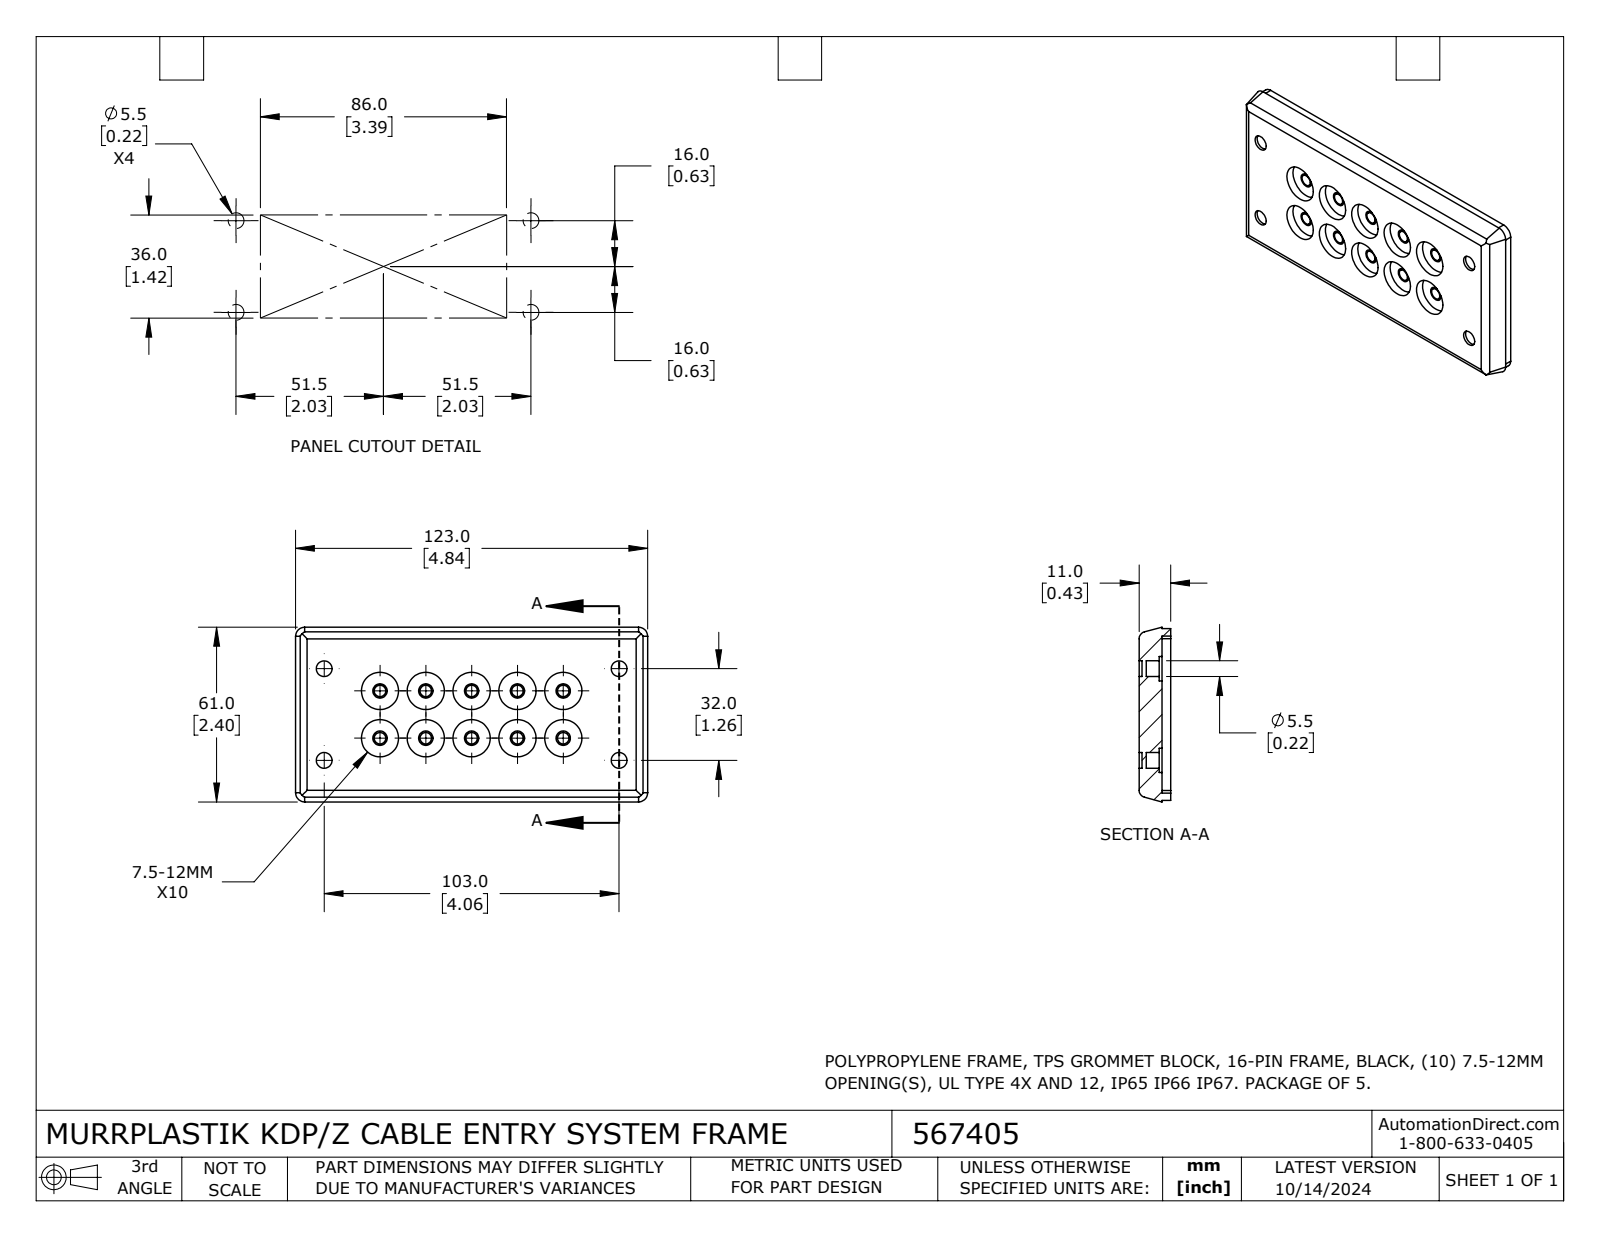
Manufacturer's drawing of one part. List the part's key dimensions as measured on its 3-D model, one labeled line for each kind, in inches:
Part name (STEP PRODUCT): 567405
STEP written by: SolidWorks 2023 (CONFIG_CONTROL_DESIGN)
Units: inches
Bodies: 1 solid, 190 faces (72 planar, 114 cylindrical, 4 other)
Overall size (bounding box): 4.843 × 2.402 × 0.433
Volume: 2.686 in³ · Surface area: 36.29 in²
Round holes (diameter × count): ⌀0.197 ×10, ⌀0.512 ×10, ⌀0.217 ×4, ⌀0.335 ×4
Round bosses / shafts (diameter × count): ⌀0.157 ×10
Partial cylindrical surfaces — rounded edges, fillets, slot ends (radius × count): R0.012 ×8, R0.035 ×4, R0.098 ×4, R0.138 ×4, R0.244 ×4, R0.266 ×4
Main face-to-face distances: 0.217, 0.098, 0.315, 0.118, 0.197, 0.433, 0.102, 0.386, 1.976, 2.26
Hole centre spacings: 0.63, 0.905, 1.26, 1.417, 0.65, 0.826, 1.225, 1.431
